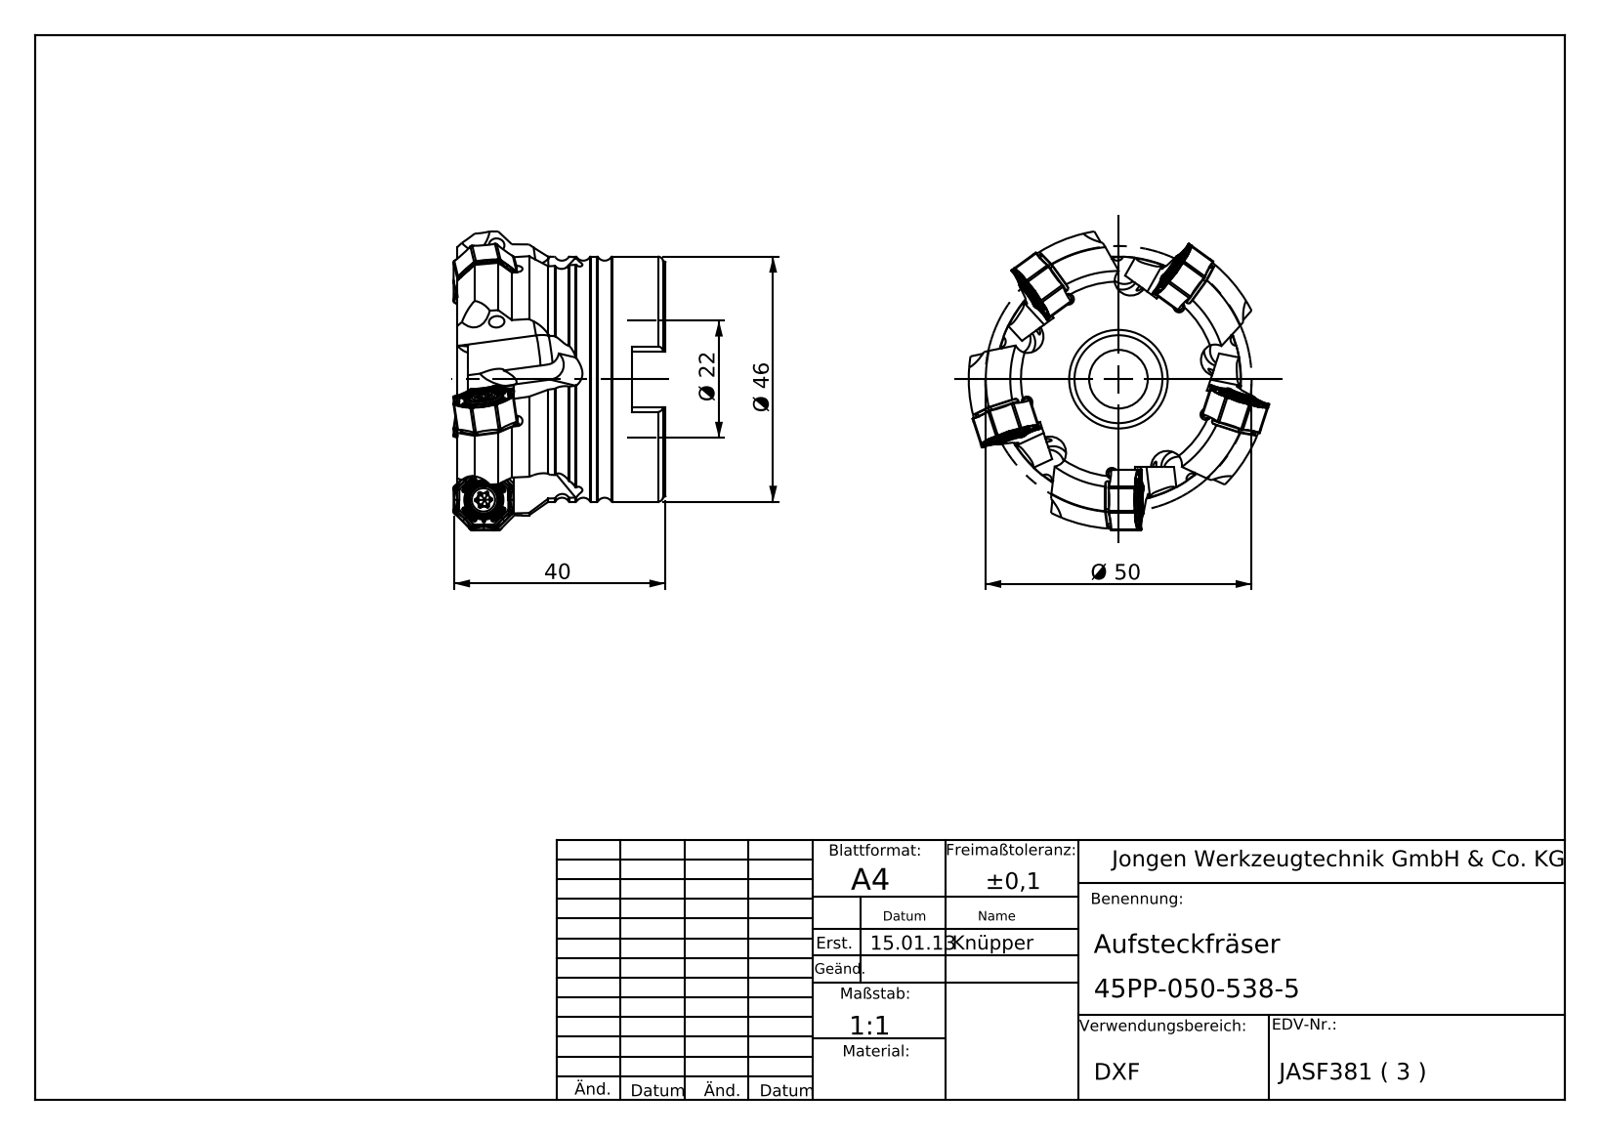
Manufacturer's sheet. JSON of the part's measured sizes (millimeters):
{"part_name": "45PP_050_538_5", "step_written_by": "SolidWorks 2014 (AUTOMOTIVE_DESIGN)", "units": "millimeters", "bodies": {"solids": 1, "faces": 240, "planar": 80, "cylindrical": 57, "other": 103}, "overall_size": [56.98, 56.98, 40.02], "volume_mm3": 56217, "surface_area_mm2": 15628, "round_holes": [[3, 5], [11, 1], [16.5, 1], [22, 1], [22.15, 1], [22.3, 1]], "round_bosses_or_shafts": [[46, 1]], "partial_cylinders_radius": [[1, 15], [1.25, 5], [3, 5], [25.55, 1], [28.1, 1]], "face_to_face_distances": [37.1, 6.25, 30.85, 19.95, 13.7, 17.15, 0.47, 10.4, 26.1, 19.85]}
